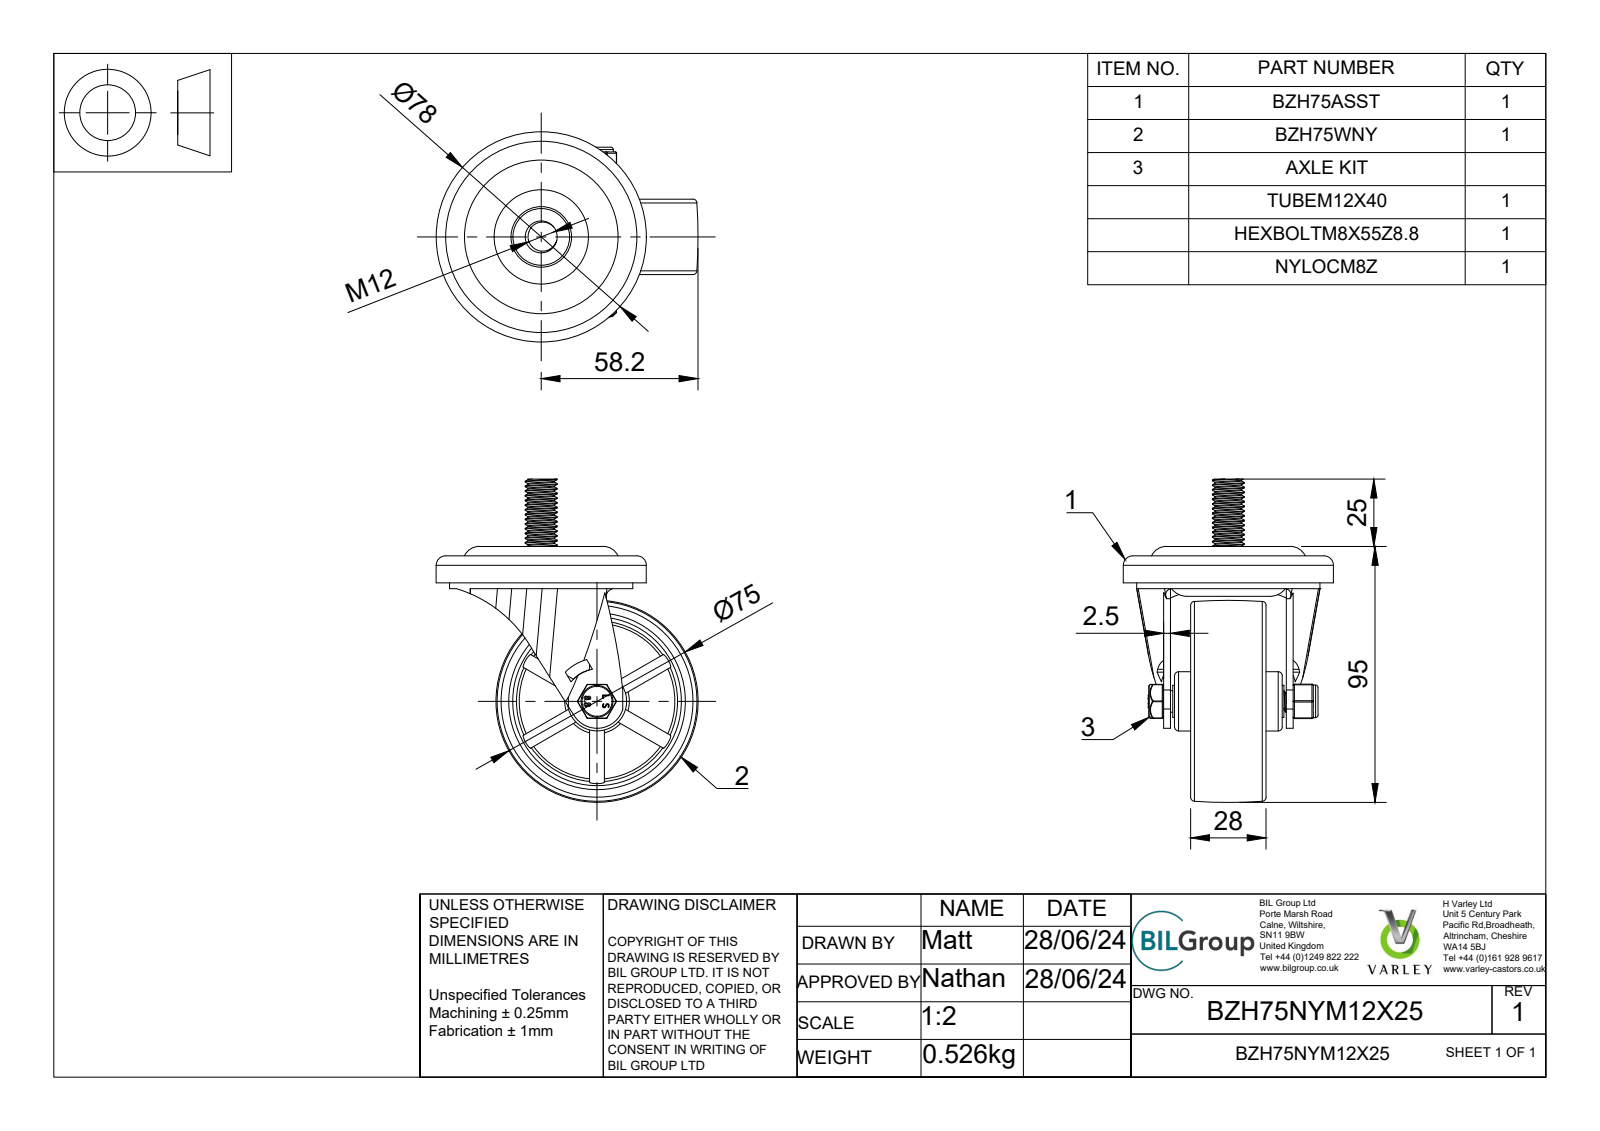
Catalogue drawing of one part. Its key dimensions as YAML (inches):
part_name: "BZH75NYM12X25 v3; BZH75ASST v2; ZINC PLATED, PRESSED STEEL HEAD; ZINC PLATED, PRESSED STEEL FORKS (+8 more)"
step_written_by: "Autodesk Translation Framework v13.14.0.145 (AUTOMOTIVE_DESIGN)"
units: inches
bodies: {solids: 8, faces: 481, planar: 176, cylindrical: 176, other: 129}
overall_size: [4.724, 3.827, 3.071]
volume: 7.35
surface_area: 103.2
round_holes:
  - {diameter: 0.026, count: 2}
  - {diameter: 0.315, count: 1}
  - {diameter: 0.323, count: 1}
  - {diameter: 0.331, count: 1}
  - {diameter: 0.339, count: 1}
  - {diameter: 0.488, count: 1}
  - {diameter: 0.61, count: 1}
  - {diameter: 1.654, count: 1}
  - {diameter: 2.48, count: 1}
  - {diameter: 2.874, count: 1}
round_bosses_or_shafts:
  - {diameter: 3.071, count: 1}
  - {diameter: 2.677, count: 1}
  - {diameter: 1.732, count: 1}
  - {diameter: 0.866, count: 1}
  - {diameter: 0.827, count: 1}
  - {diameter: 0.669, count: 1}
  - {diameter: 0.63, count: 1}
  - {diameter: 0.476, count: 1}
partial_cylinders:
  - {radius: 0.02, count: 18}
  - {radius: 0.01, count: 12}
  - {radius: 0.108, count: 8}
  - {radius: 0.013, count: 4}
  - {radius: 0.025, count: 4}
  - {radius: 0.025, count: 2}
  - {radius: 0.025, count: 2}
  - {radius: 0.118, count: 2}
face_to_face_distances: [0.098, 0.236, 0.148, 0.295, 0.669, 0.433, 0.395, 0.828, 1.065, 1.498]
hole_center_spacings: [0.127, 0.098]
